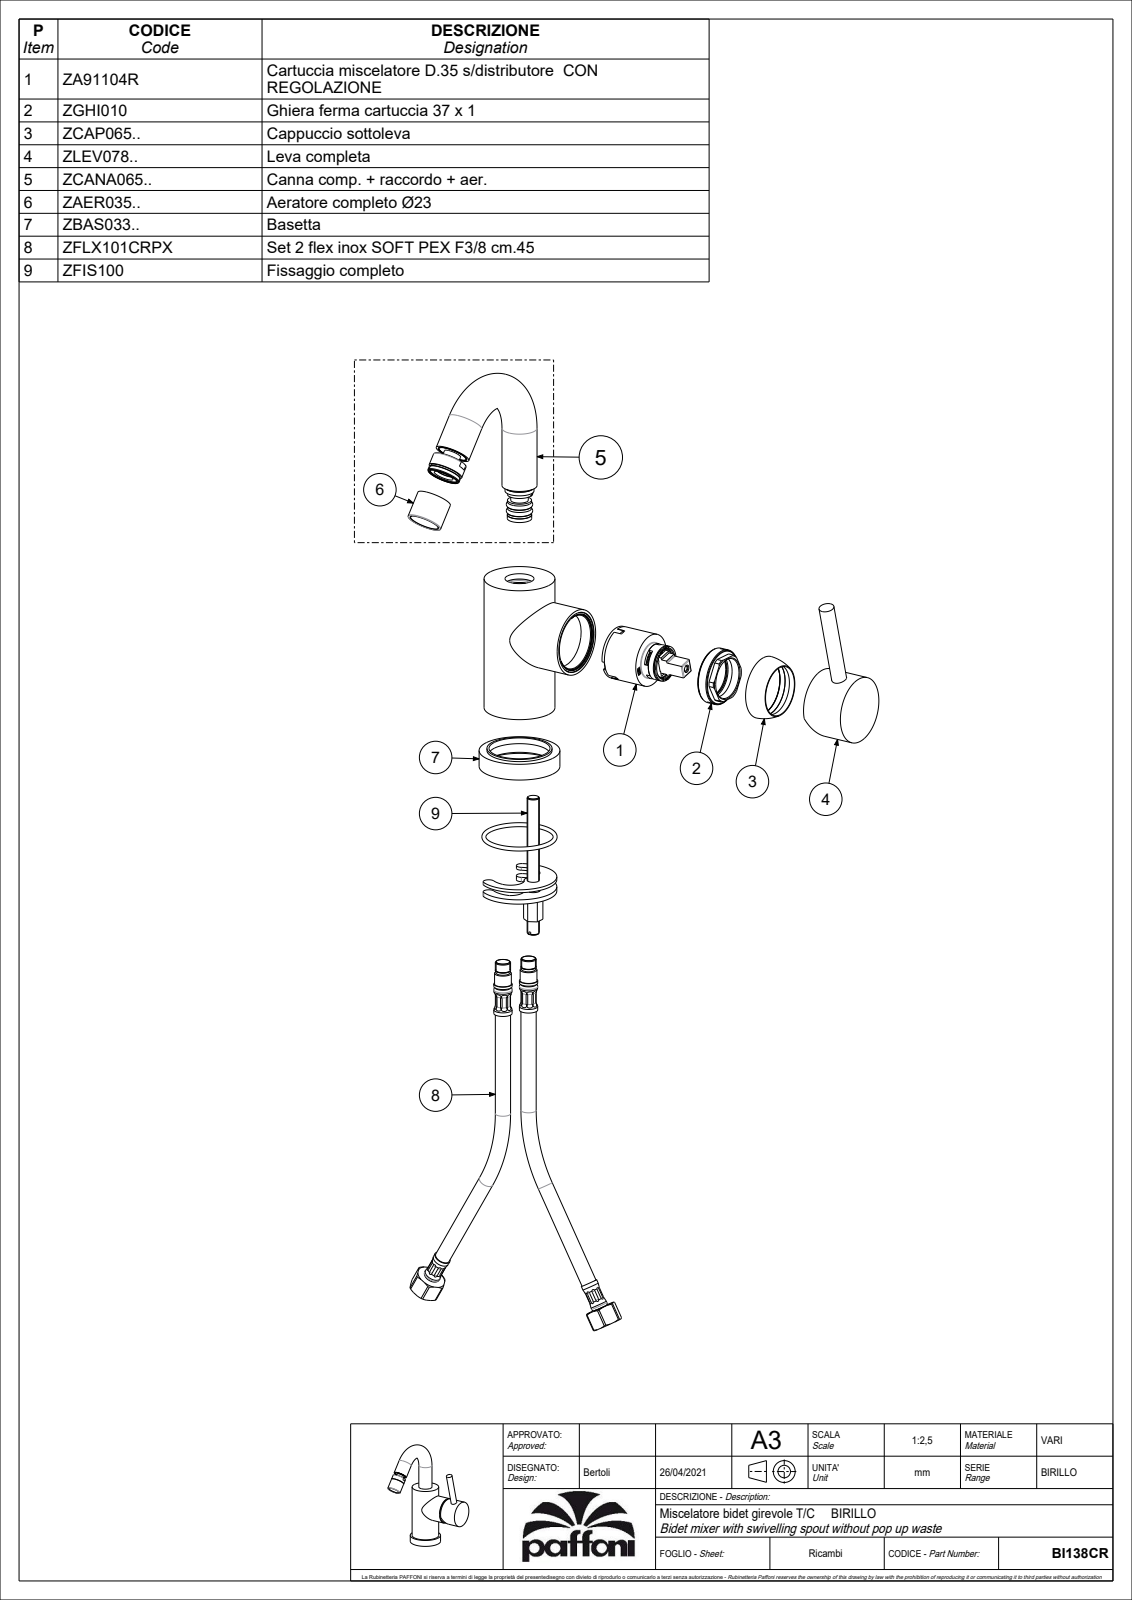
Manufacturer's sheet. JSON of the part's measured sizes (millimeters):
{"part_name": "BI138CR", "step_written_by": "CREO PARAMETRIC BY PTC INC, 2020044 (CONFIG_CONTROL_DESIGN)", "units": "millimeters", "bodies": {"solids": 3, "faces": 1154, "planar": 647, "cylindrical": 312, "other": 195}, "overall_size": [187.6, 131.23, 104.35], "volume_mm3": 191449, "surface_area_mm2": 96809, "round_holes": [[6.5, 3], [9, 3], [18, 3], [19, 3], [4, 2], [5.5, 2], [10, 2], [11, 2], [40, 2], [3.3, 1], [5, 1], [6.8, 1]], "round_bosses_or_shafts": [[23, 3], [53, 1], [46.5, 1], [44, 1], [42.7, 1], [36.8, 1], [35, 1], [34.8, 1]], "partial_cylinders_radius": [[0.5, 27], [0.15, 11], [0.3, 4], [1, 2], [1.05, 1], [2.1, 1], [4.25, 1], [7, 1]], "face_to_face_distances": [9, 75, 1.5, 15, 2, 24, 56.3, 25.5, 0.5, 4], "hole_center_spacings": [10.97, 20.43, 1.2, 5, 9.18, 9.27, 10.18, 11]}
